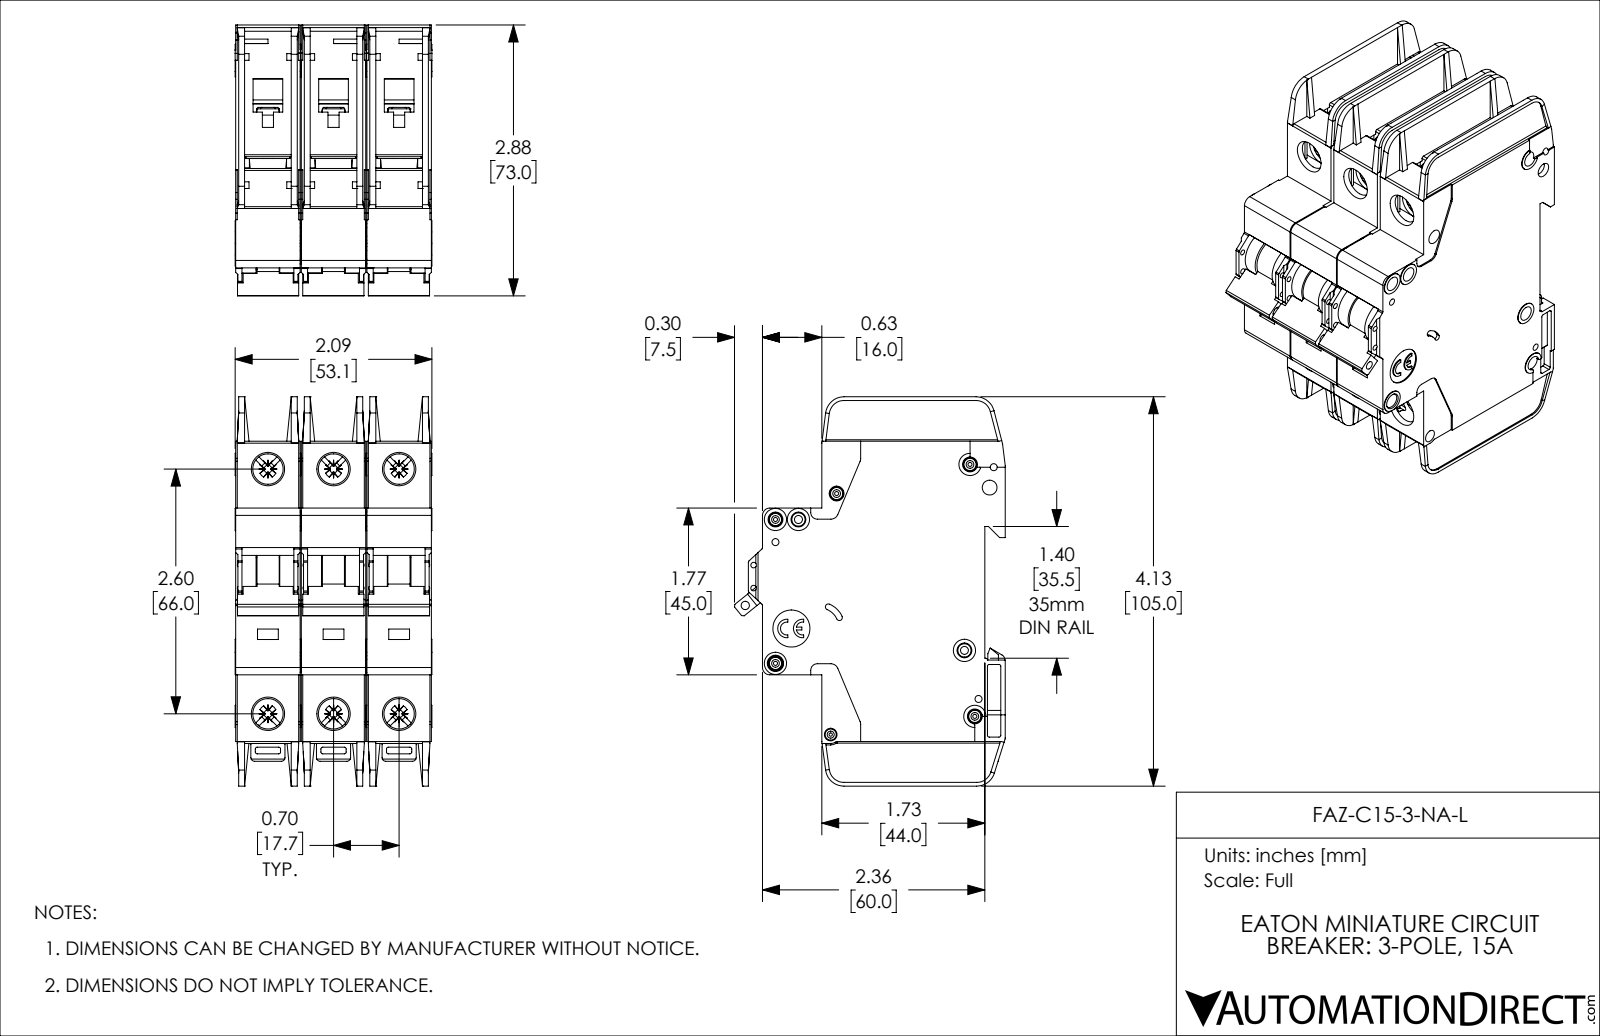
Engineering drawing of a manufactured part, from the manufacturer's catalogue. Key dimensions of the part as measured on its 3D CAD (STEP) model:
Part name (STEP PRODUCT): FAZ-C15-3-NA-L
STEP written by: SolidWorks 2019 (AUTOMOTIVE_DESIGN)
Units: inches
Bodies: 3 solids, 3381 faces (2013 planar, 1071 cylindrical, 297 other)
Overall size (bounding box): 4.134 × 2.876 × 2.091
Volume: 14.05 in³ · Surface area: 123 in²
Round holes (diameter × count): ⌀0.157 ×8, ⌀0.323 ×6, ⌀0.043 ×5, ⌀0.075 ×4, ⌀0.059 ×2, ⌀0.085 ×2, ⌀0.035 ×1, ⌀0.089 ×1, ⌀0.098 ×1, ⌀0.134 ×1, ⌀0.394 ×1
Round bosses / shafts (diameter × count): ⌀0.13 ×5, ⌀0.236 ×4, ⌀0.118 ×4, ⌀0.098 ×3
Partial cylindrical surfaces — rounded edges, fillets, slot ends (radius × count): R0.02 ×72, R0.016 ×30, R0.039 ×18, R0.043 ×12, R0.079 ×12, R0.008 ×6, R0.01 ×6, R0.028 ×6
Main face-to-face distances: 0.697, 0.047, 1.394, 0.685, 0.591, 1.382, 0.744, 0.65, 0.106, 0.094
Hole centre spacings: 0.697, 2.69, 2.598, 0.244, 0.537, 0.87, 1.394, 2.948
